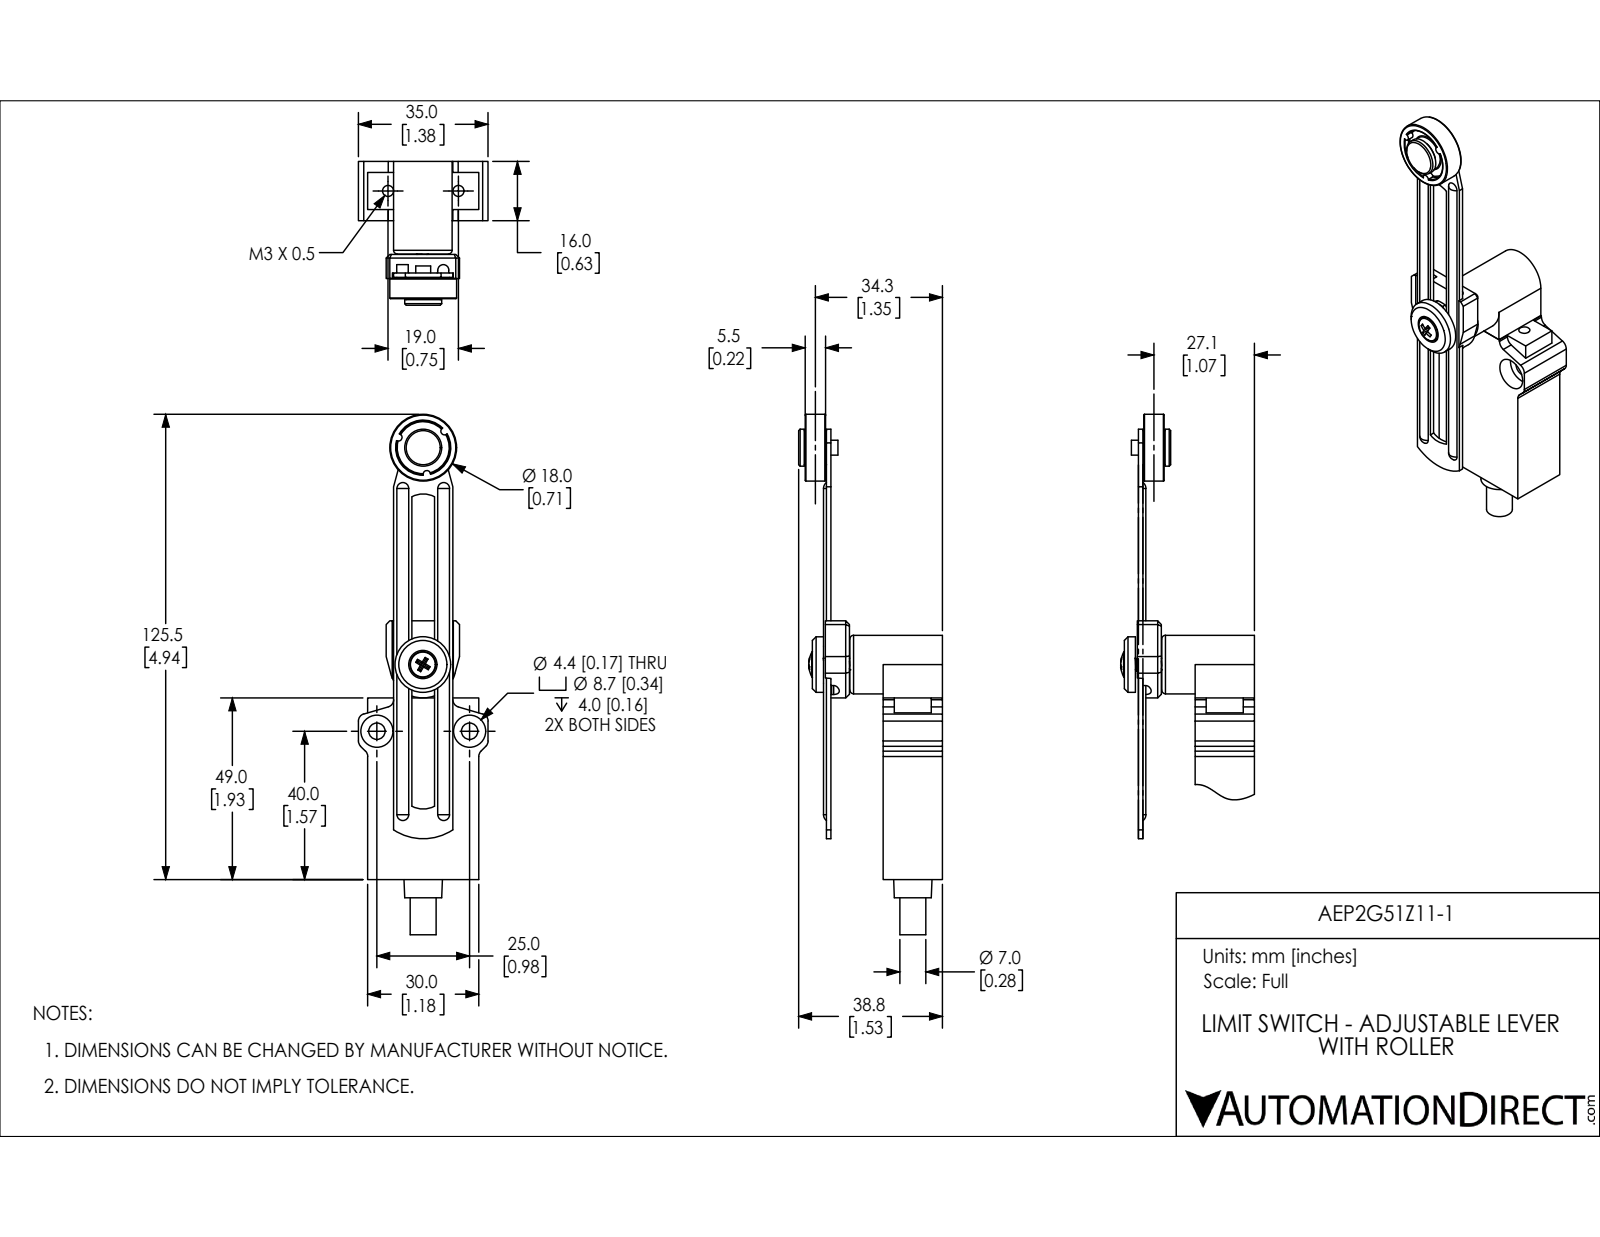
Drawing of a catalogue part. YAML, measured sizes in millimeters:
part_name: "AEP2G51Z11-1"
step_written_by: "SolidWorks 2018 (AUTOMOTIVE_DESIGN)"
units: millimeters
bodies: {solids: 8, faces: 486, planar: 194, cylindrical: 226, other: 66}
overall_size: [140.4, 38.8, 35]
volume: 33020
surface_area: 15520
round_holes:
  - {diameter: 3, count: 2}
  - {diameter: 4.1, count: 2}
  - {diameter: 4.4, count: 2}
  - {diameter: 8.7, count: 2}
  - {diameter: 2.5, count: 1}
  - {diameter: 5, count: 1}
  - {diameter: 5.7, count: 1}
  - {diameter: 6.1, count: 1}
  - {diameter: 7.6, count: 1}
round_bosses_or_shafts:
  - {diameter: 7, count: 2}
  - {diameter: 18, count: 1}
  - {diameter: 15.8, count: 1}
  - {diameter: 15, count: 1}
  - {diameter: 10, count: 1}
  - {diameter: 6, count: 1}
  - {diameter: 4, count: 1}
  - {diameter: 3.5, count: 1}
partial_cylinders:
  - {radius: 0.2, count: 36}
  - {radius: 2, count: 10}
  - {radius: 0.2, count: 4}
  - {radius: 1.2, count: 4}
  - {radius: 1, count: 3}
  - {radius: 6.5, count: 3}
  - {radius: 0.8, count: 2}
  - {radius: 1.5, count: 1}
face_to_face_distances: [16, 1.2, 14.1, 30.1, 31.3, 15.3, 30, 7, 2, 49]
hole_center_spacings: [77.5, 19, 21.9, 22, 25, 58.5]
